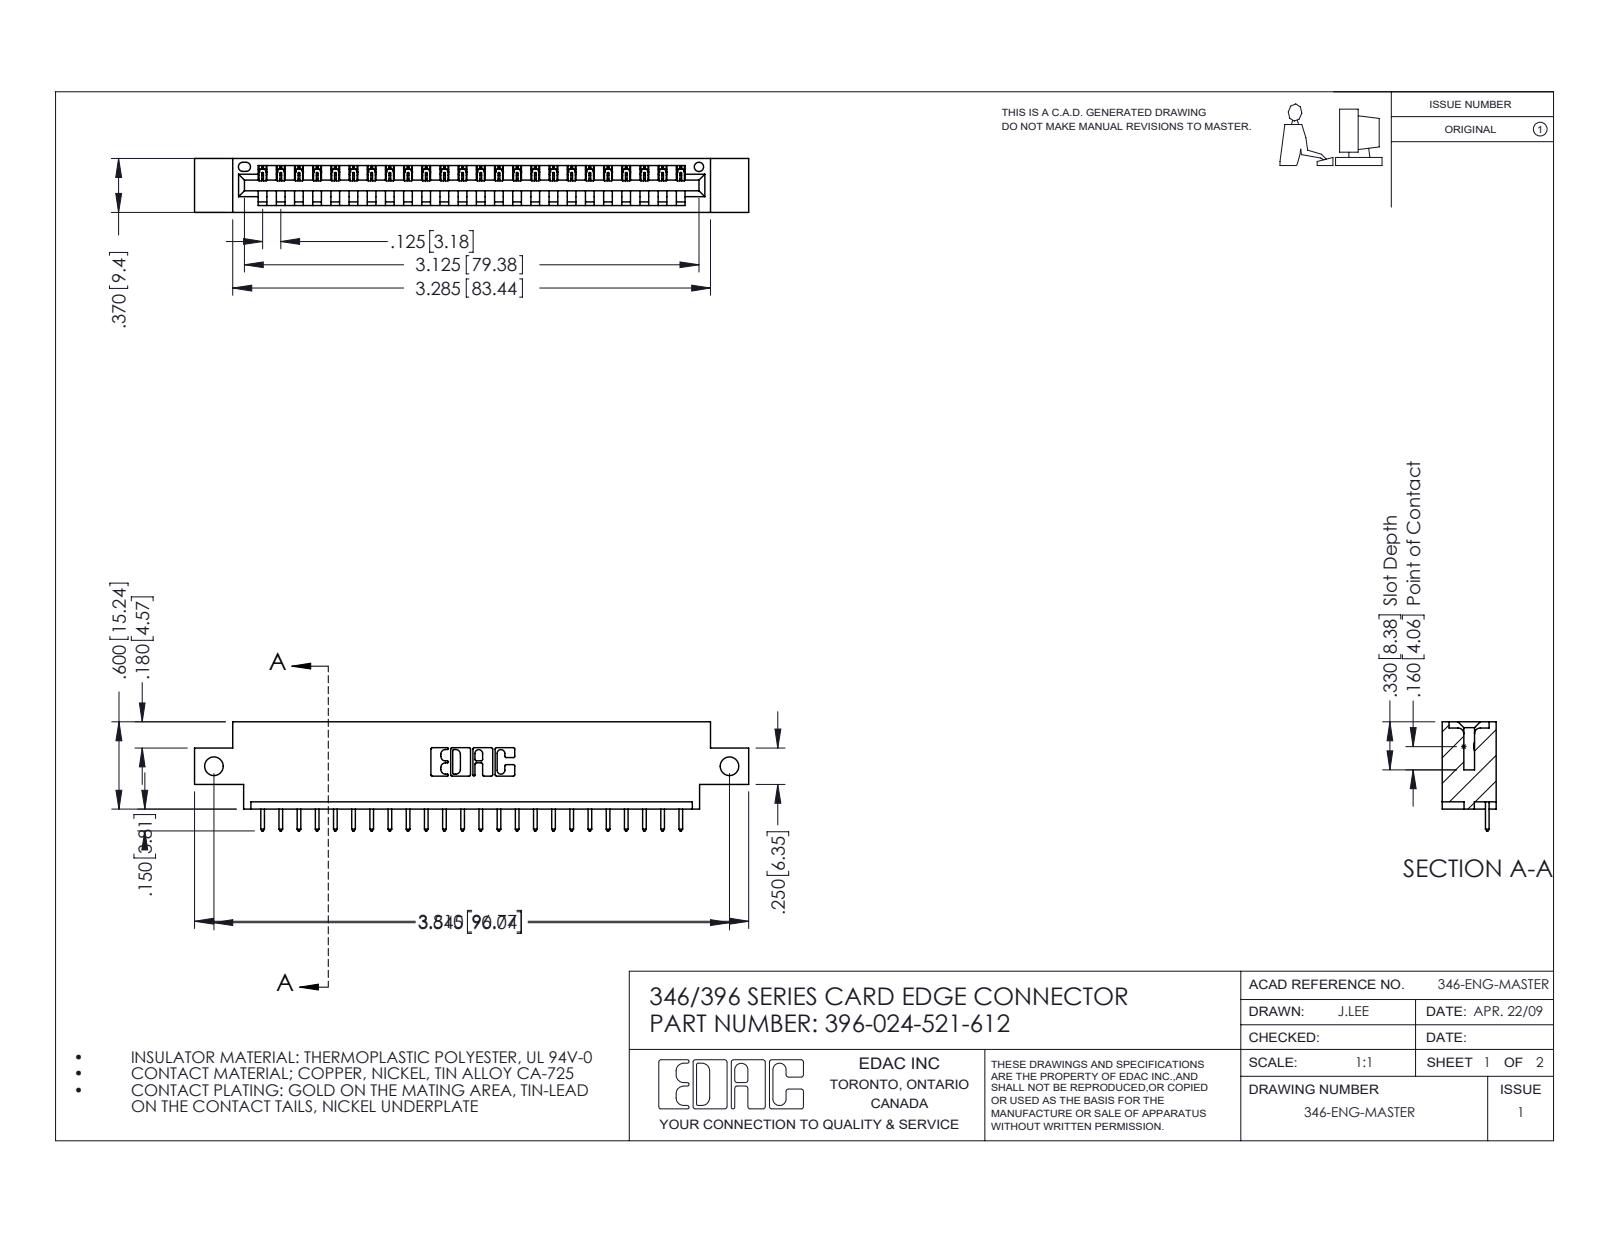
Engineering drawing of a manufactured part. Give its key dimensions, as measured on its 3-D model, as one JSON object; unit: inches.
{"part_name": "345-292-001_345-293-121; 346 Part_0.170 Offset - Side Mount; 396-024-521-612", "step_written_by": "SolidWorks 2016 (CONFIG_CONTROL_DESIGN)", "units": "inches", "bodies": {"solids": 25, "faces": 1518, "planar": 1040, "cylindrical": 478, "other": 0}, "overall_size": [3.81, 0.75, 0.37], "volume_in3": 0.539, "surface_area_in2": 16.41, "round_holes": [[0.128, 2], [0.064, 1]], "partial_cylinders_radius": [[0.006, 48], [0.01, 48], [0.01, 22], [0.007, 6], [0.031, 6], [0.026, 3], [0.031, 2], [0.04, 2]], "face_to_face_distances": [0.048, 0.322, 0.37, 0.25, 0.072, 0.298, 0.025, 0.148, 0.222, 0.1], "hole_center_spacings": [3.545]}
